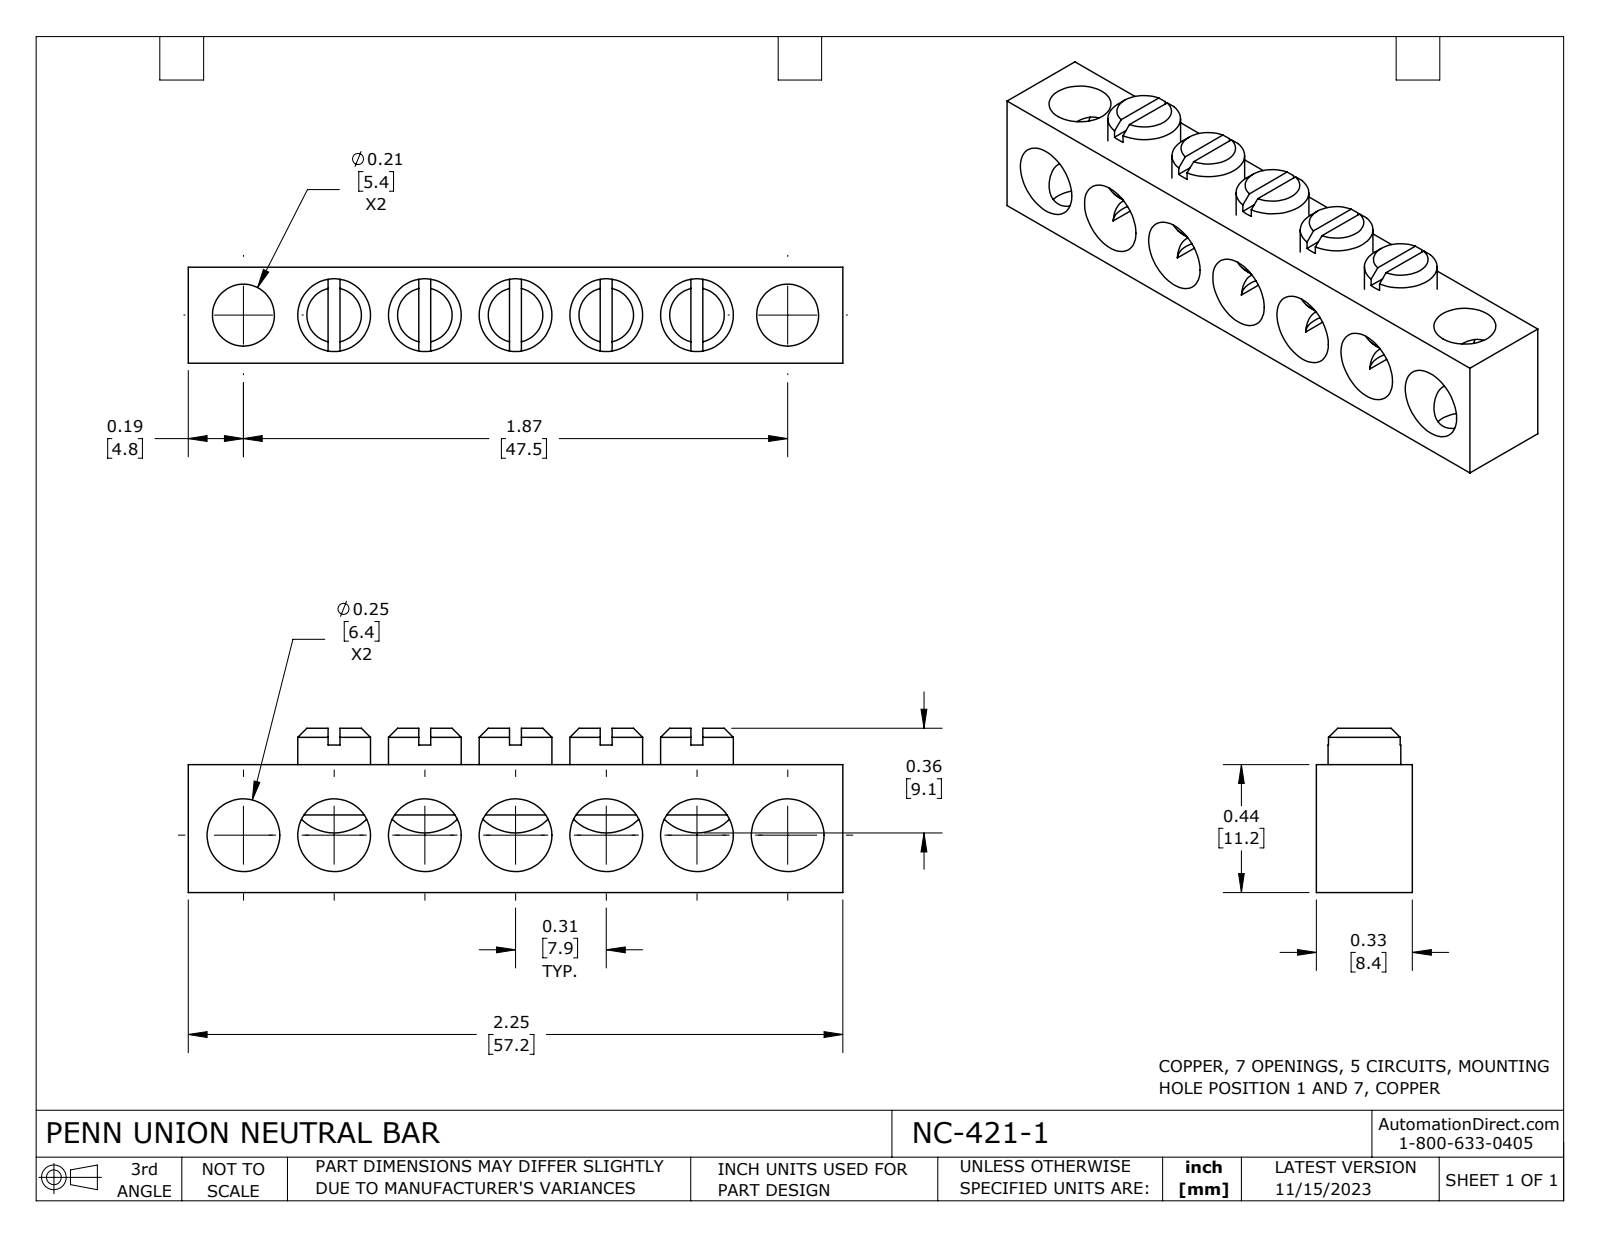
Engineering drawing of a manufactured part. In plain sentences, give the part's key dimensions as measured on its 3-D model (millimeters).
The part is named "NC-421-1". Its 3-D file was written by "SolidWorks 2023 (CONFIG_CONTROL_DESIGN)". It is 6 solids with 118 faces: 41 planar, 52 cylindrical and 25 other. Overall it measures 57.2 by 14.4 by 8.4 millimeters. Its volume is 4 110 cubic millimeters and its surface area 4 380 square millimeters. Round holes: 7 of diameter 5.4, 7 of diameter 6.4. Round bosses or shafts: 5 of diameter 6.4. The main face-to-face distances are 8.4, 11.2, 57.2, 7.9, 14.4, 3.2, 15.8, 1, 23.7, 9. The hole center spacings are 7.9, 15.8, 23.7, 31.7, 39.6, 47.5.
